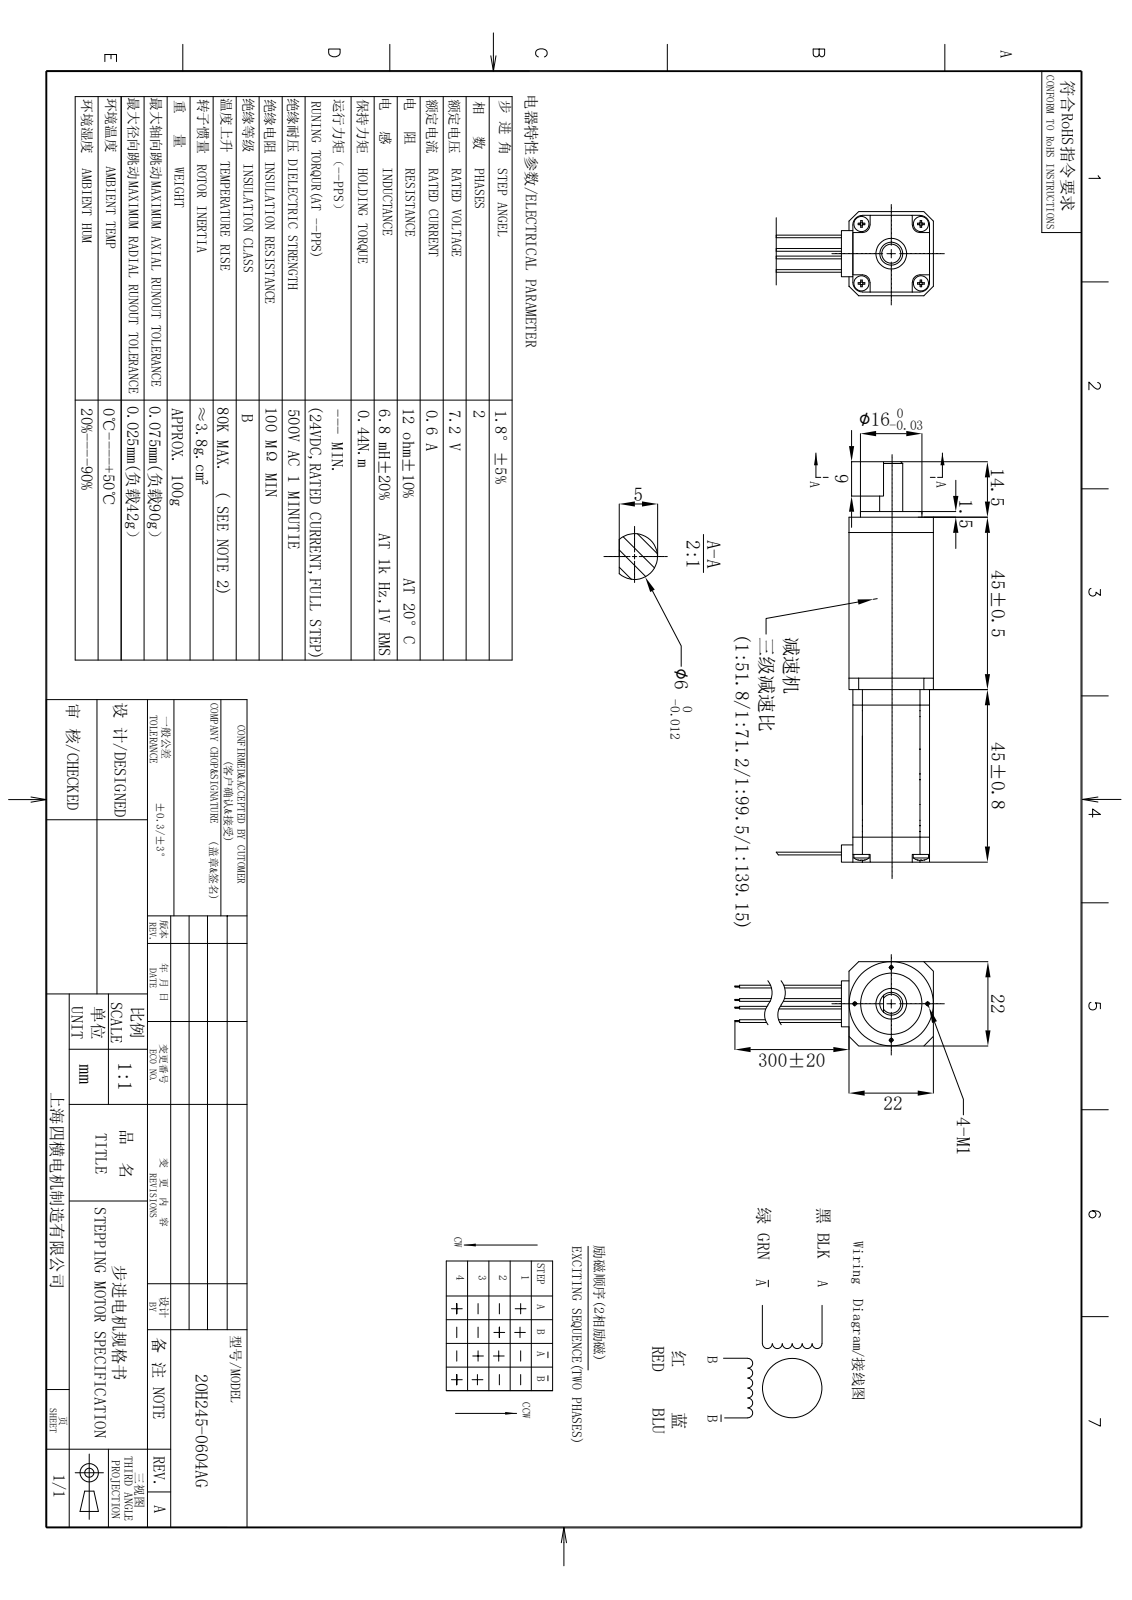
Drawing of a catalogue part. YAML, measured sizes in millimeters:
part_name: "20H245-0604AG51减速器前端盖; 20H245-0604AG51; 20H245-0604AG51减速器固定; 20H245-0604AG51电机 (+8 more)"
step_written_by: "SolidWorks 2020 (AUTOMOTIVE_DESIGN)"
units: millimeters
bodies: {solids: 20, faces: 1137, planar: 803, cylindrical: 298, other: 36}
overall_size: [104.5, 41, 22]
volume: 36262
surface_area: 16447
round_holes:
  - {diameter: 1, count: 4}
  - {diameter: 2.5, count: 4}
  - {diameter: 8, count: 1}
round_bosses_or_shafts:
  - {diameter: 4.5, count: 4}
  - {diameter: 4, count: 4}
  - {diameter: 2, count: 4}
  - {diameter: 0.7, count: 4}
  - {diameter: 22, count: 1}
  - {diameter: 16, count: 1}
  - {diameter: 6, count: 1}
partial_cylinders:
  - {radius: 0.3, count: 16}
  - {radius: 0.35, count: 4}
  - {radius: 2, count: 4}
  - {radius: 2.45, count: 4}
  - {radius: 2.5, count: 4}
face_to_face_distances: [20, 45, 41, 4, 3, 38, 7, 79.5, 34.5, 38.5]
hole_center_spacings: [7.95, 18.91, 9.5, 10.96, 13.44, 15.5, 19, 21.92]
